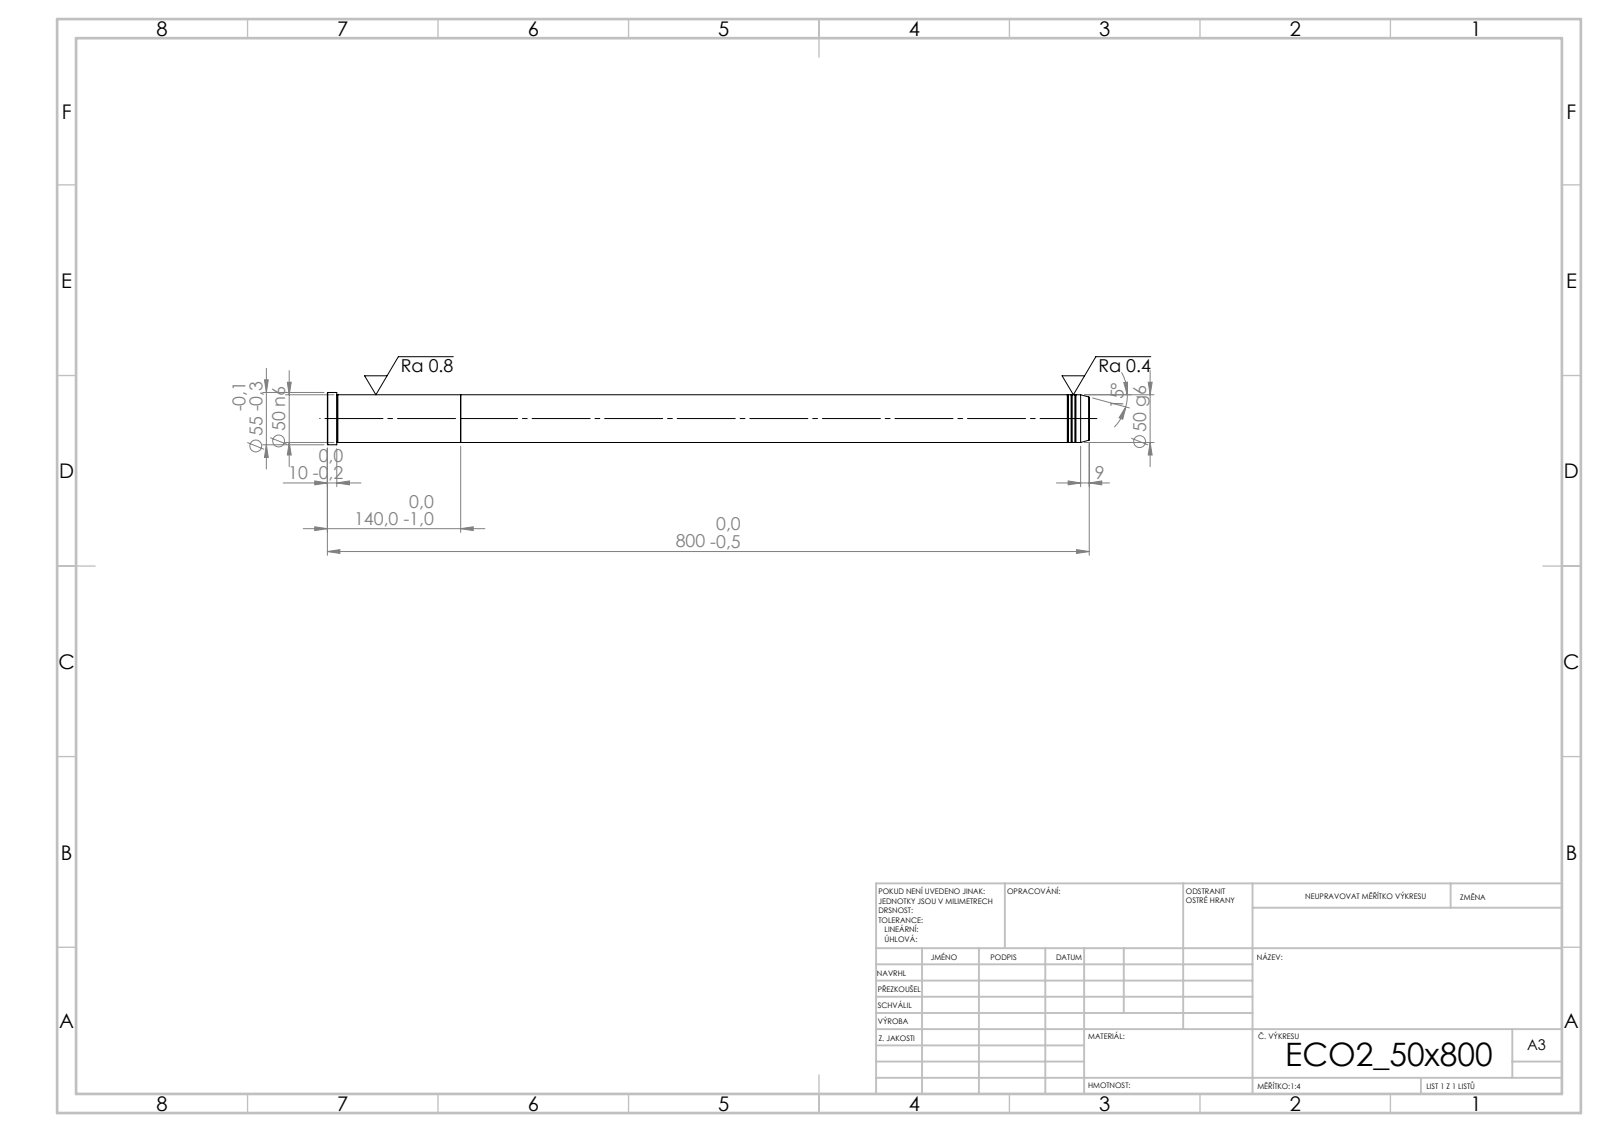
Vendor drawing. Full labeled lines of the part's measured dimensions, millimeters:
STEP written by: SolidWorks 2019 (CONFIG_CONTROL_DESIGN)
Units: millimetres
Bodies: 2 solids, 39 faces (5 planar, 12 cylindrical, 22 other)
Overall size (bounding box): 800 × 55 × 55
Volume: 1 573 000 mm³ · Surface area: 134 397 mm²
Round bosses / shafts (diameter × count): ⌀55 ×1, ⌀50 ×1
Main face-to-face distances: 140, 660, 800, 790, 130, 10
